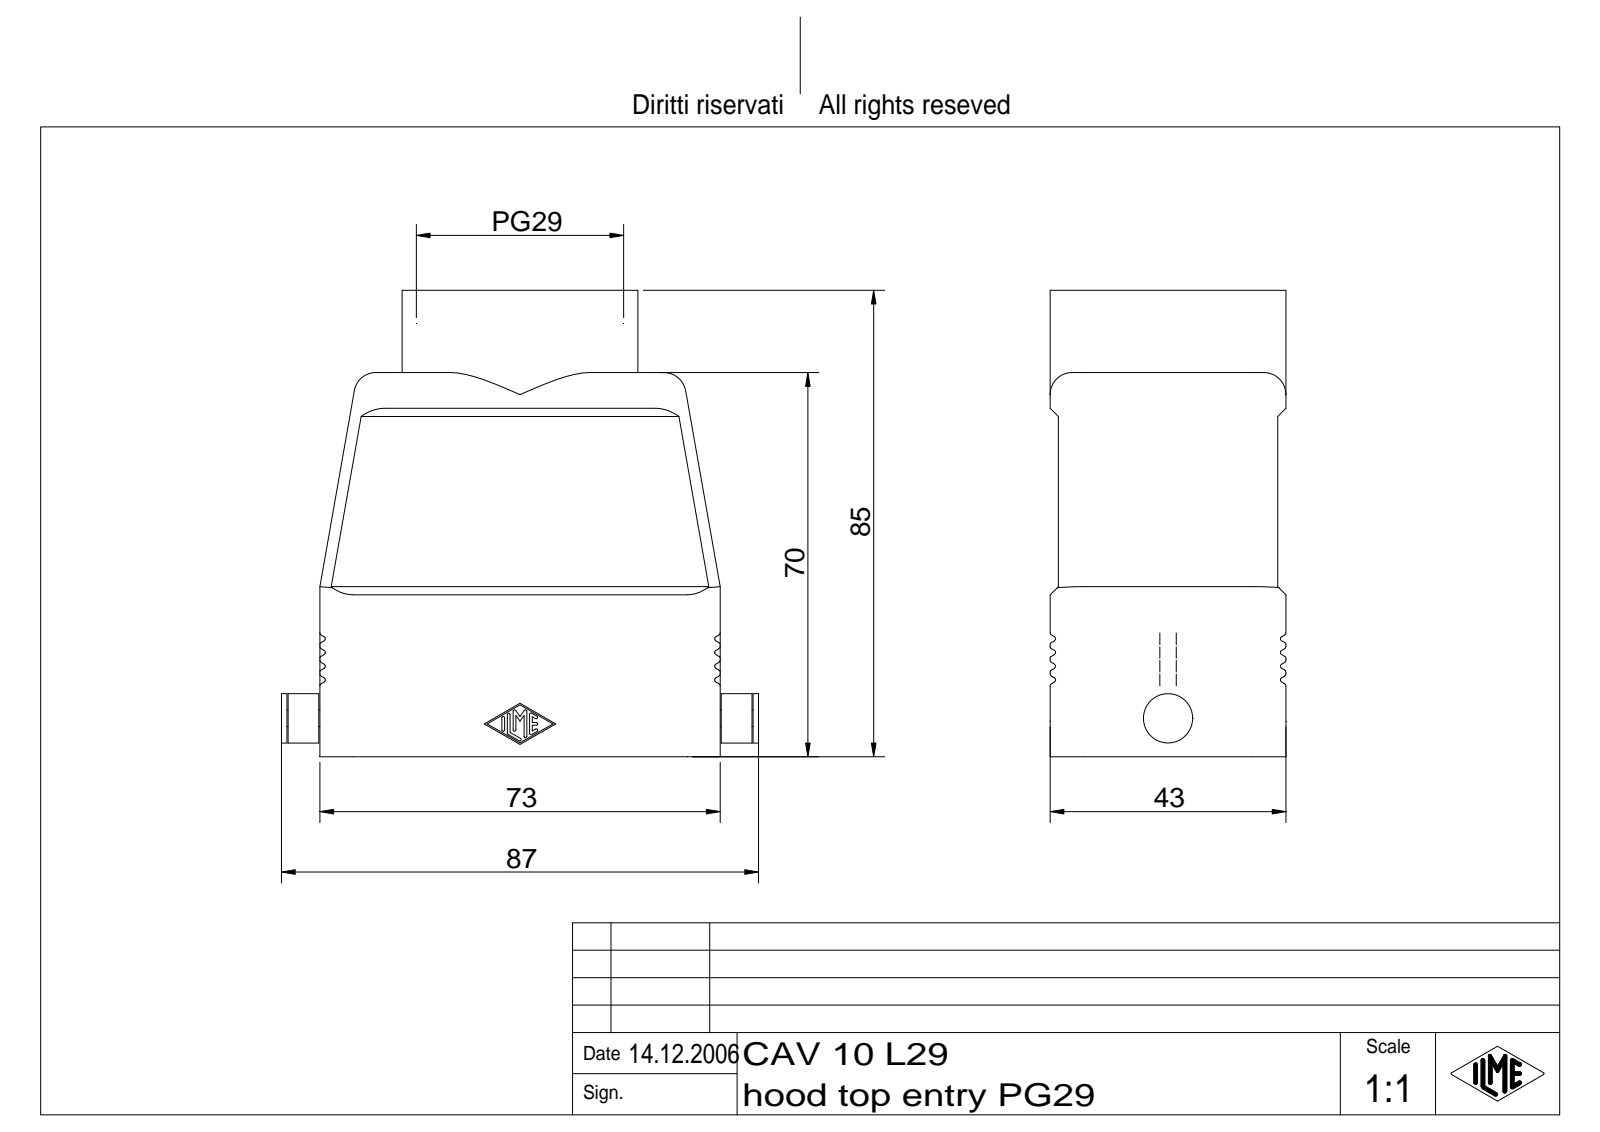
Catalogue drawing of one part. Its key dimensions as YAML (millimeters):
part_name: "CAV 10 L29"
step_written_by: "Autodesk Inventor 7 (AUTOMOTIVE_DESIGN)"
units: millimeters
bodies: {solids: 1, faces: 643, planar: 129, cylindrical: 312, other: 202}
overall_size: [87, 85, 43]
volume: 58525
surface_area: 40858
round_holes:
  - {diameter: 33.7, count: 1}
  - {diameter: 35.48, count: 1}
round_bosses_or_shafts:
  - {diameter: 43, count: 1}
  - {diameter: 9, count: 1}
  - {diameter: 3, count: 1}
partial_cylinders:
  - {radius: 0.4, count: 64}
  - {radius: 0.25, count: 14}
  - {radius: 3, count: 8}
  - {radius: 6, count: 8}
  - {radius: 2, count: 4}
  - {radius: 4, count: 4}
  - {radius: 5, count: 2}
face_to_face_distances: [1.5, 3, 40, 38.5, 37, 41.5, 70, 67, 43, 8.5]
